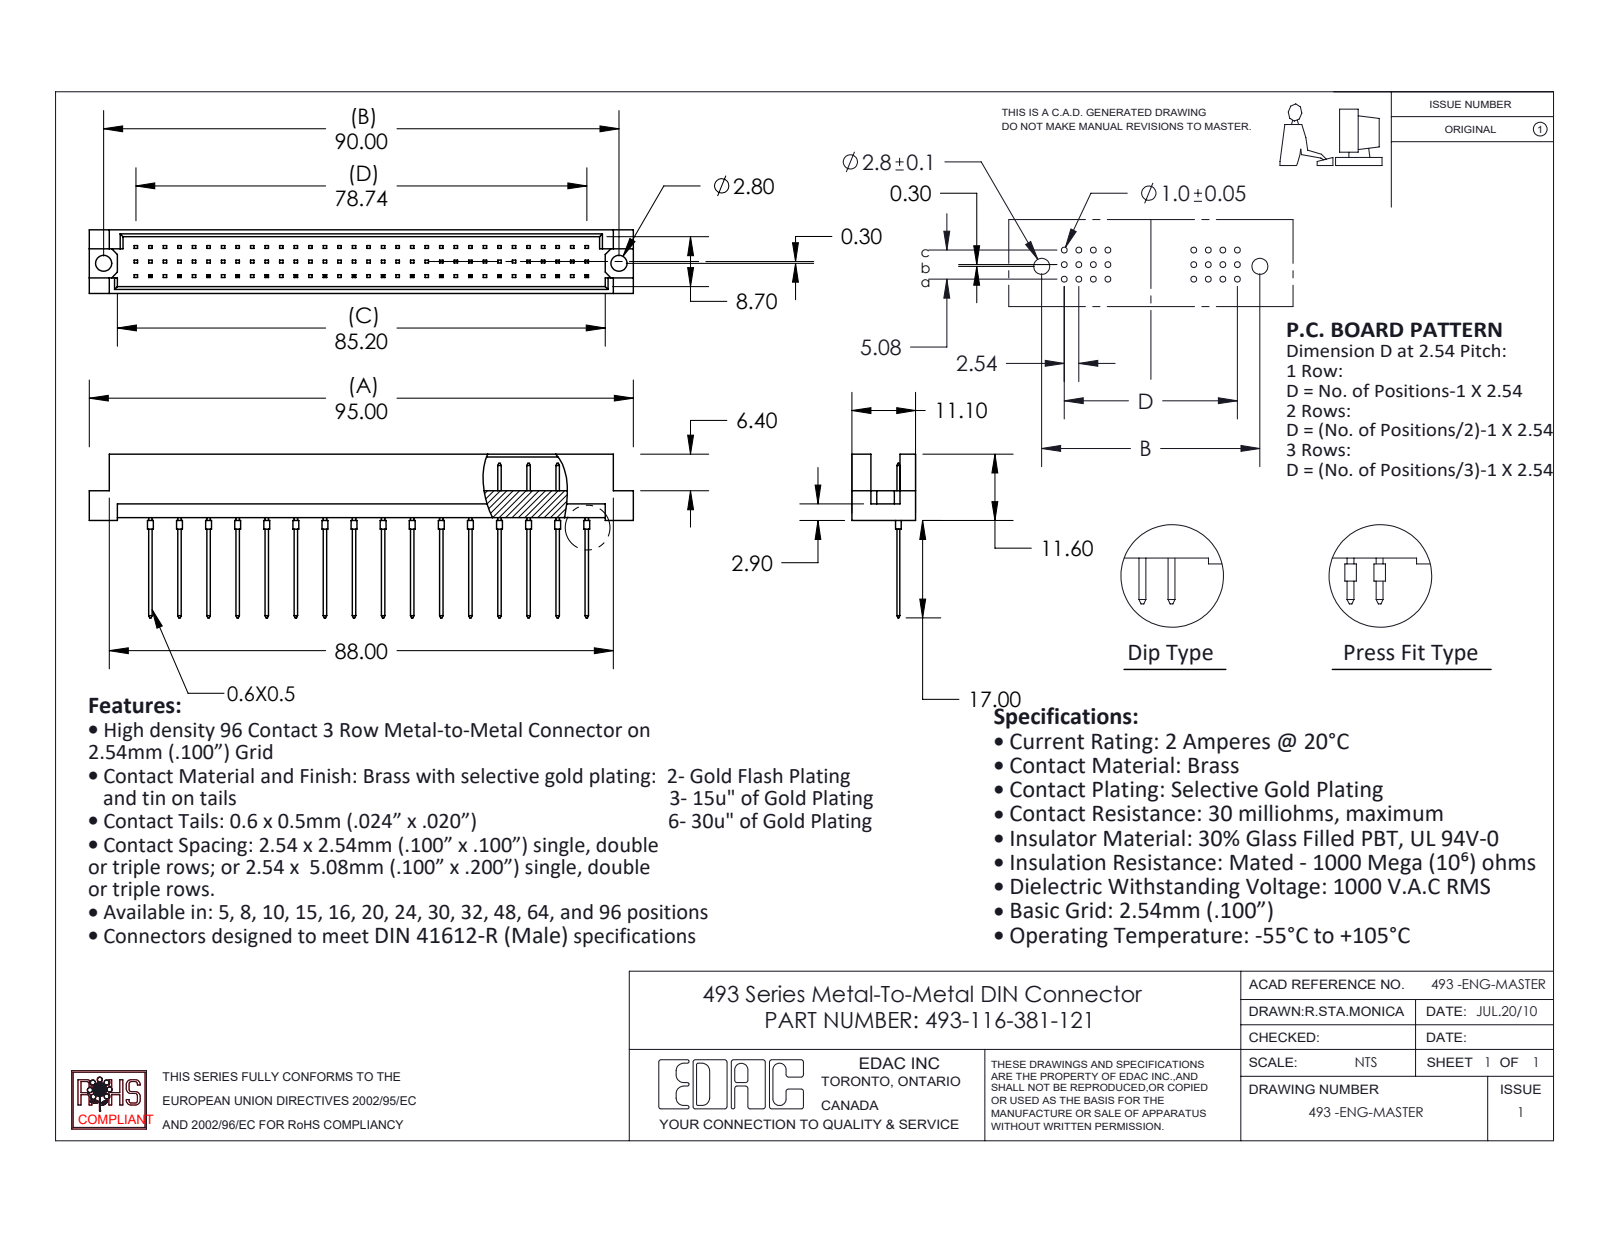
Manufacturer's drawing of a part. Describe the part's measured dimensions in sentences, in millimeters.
The part is named "493-290_81; 493-116-381-621; 493 Part_96". Its 3-D file was written by "SolidWorks 2020 (CONFIG_CONTROL_DESIGN)". It is 17 solids with 788 faces: 752 planar, 36 cylindrical and 0 other. Overall it measures 95 by 28.6 by 11.1 millimeters. Its volume is 5 799 cubic millimeters and its surface area 7 457 square millimeters. Round holes: 2 of diameter 2.8. Round bosses or shafts: 16 of diameter 1. The main face-to-face distances are 1.2, 9.9, 11.1, 8.7, 4.7, 0.5, 5.08, 3.26, 7.84, 2.06. The hole center spacings are 90.
